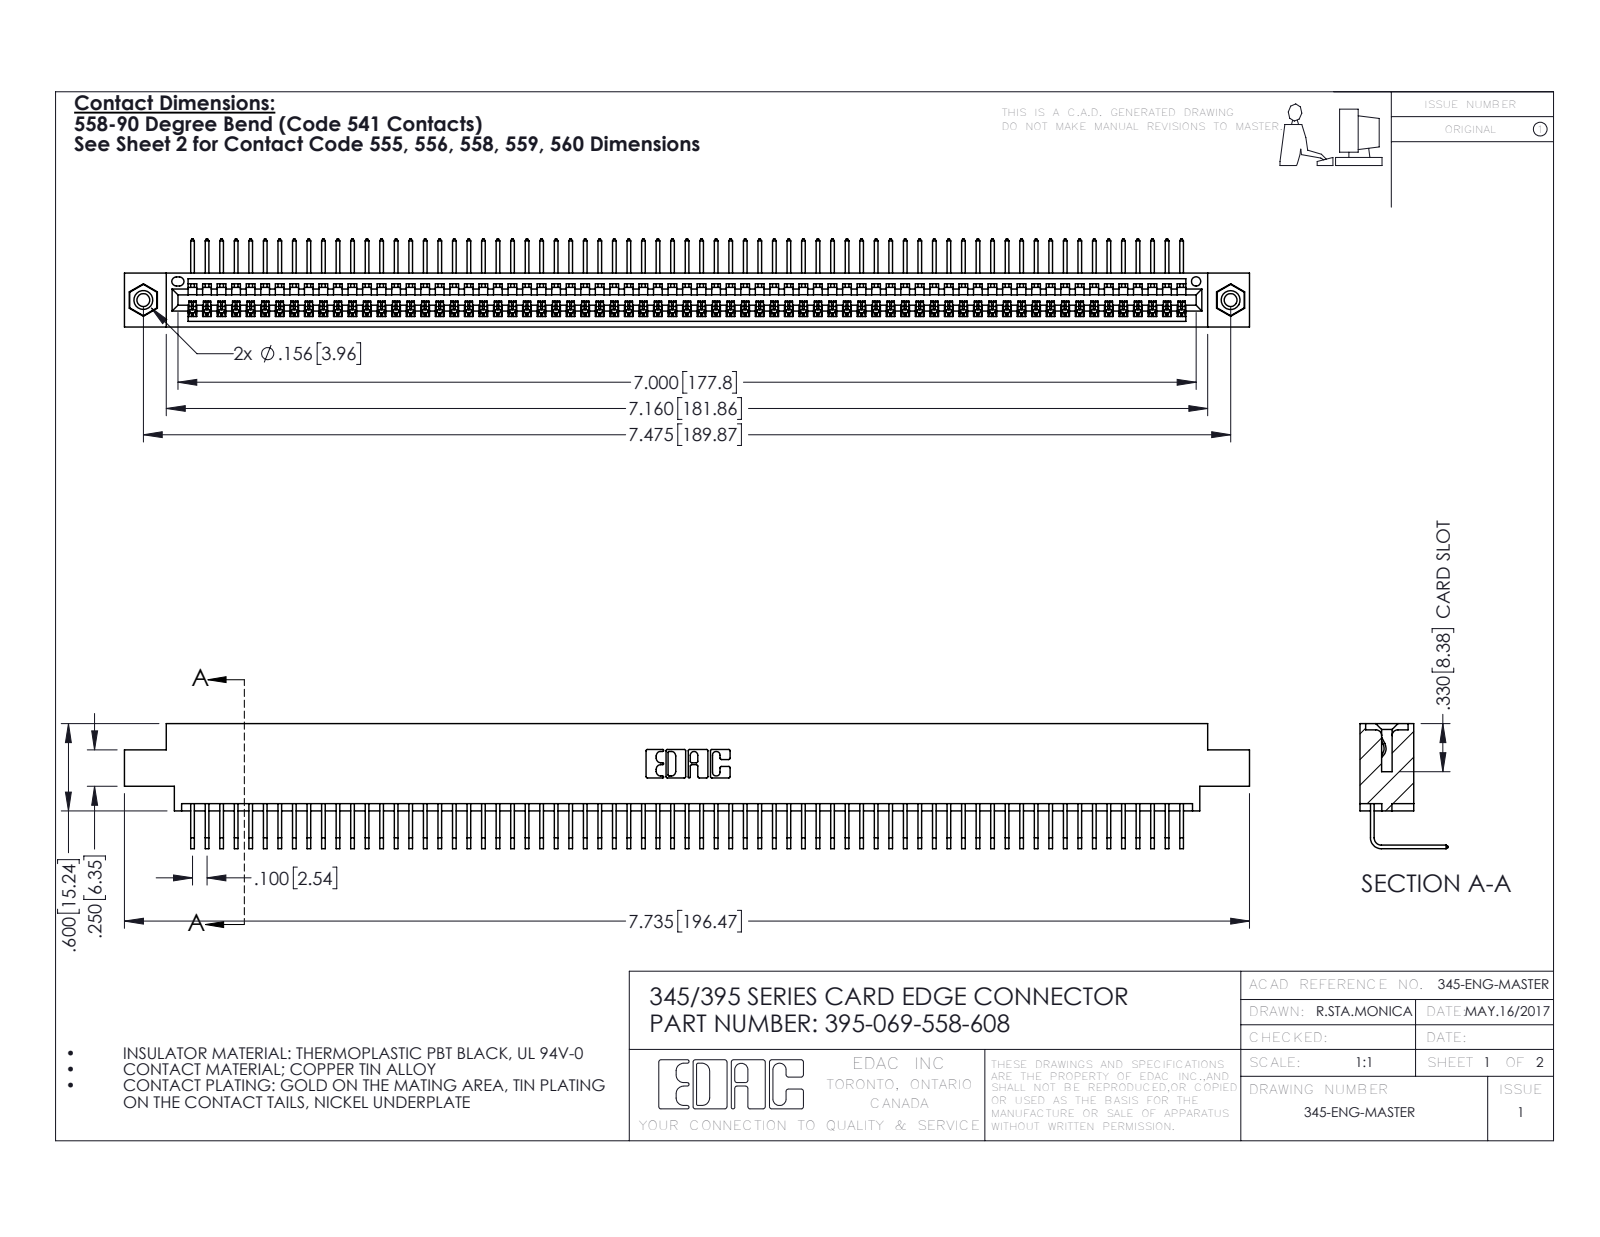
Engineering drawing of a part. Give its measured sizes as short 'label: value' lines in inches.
name: 395-069-558-608; 345-250-001_345-250-003-102; 345 Part_0.170 Offset - 0.156 Dia-TI; 345-292-001_558 Tail - 2
written by: SolidWorks 2016 (CONFIG_CONTROL_DESIGN)
unit: in
bodies: 72 solids, 4330 faces (3014 planar, 1300 cylindrical, 16 other)
size: 7.735 × 0.859 × 0.605
volume: 1.159 in³; area: 42.01 in²
holes: 2× ⌀0.089, 2× ⌀0.125, 2× ⌀0.156, 1× ⌀0.064
bosses: 2× ⌀0.155
rounds: 138× R0.006, 22× R0.01, 6× R0.007, 6× R0.031, 3× R0.026, 2× R0.031, 2× R0.04, 1× R0.014
face distances: 0.072, 0.298, 0.37, 0.2, 0.098, 0.272, 0.025, 0.225, 0.175, 0.149
hole spacings: 0.27, 7.239, 7.475
